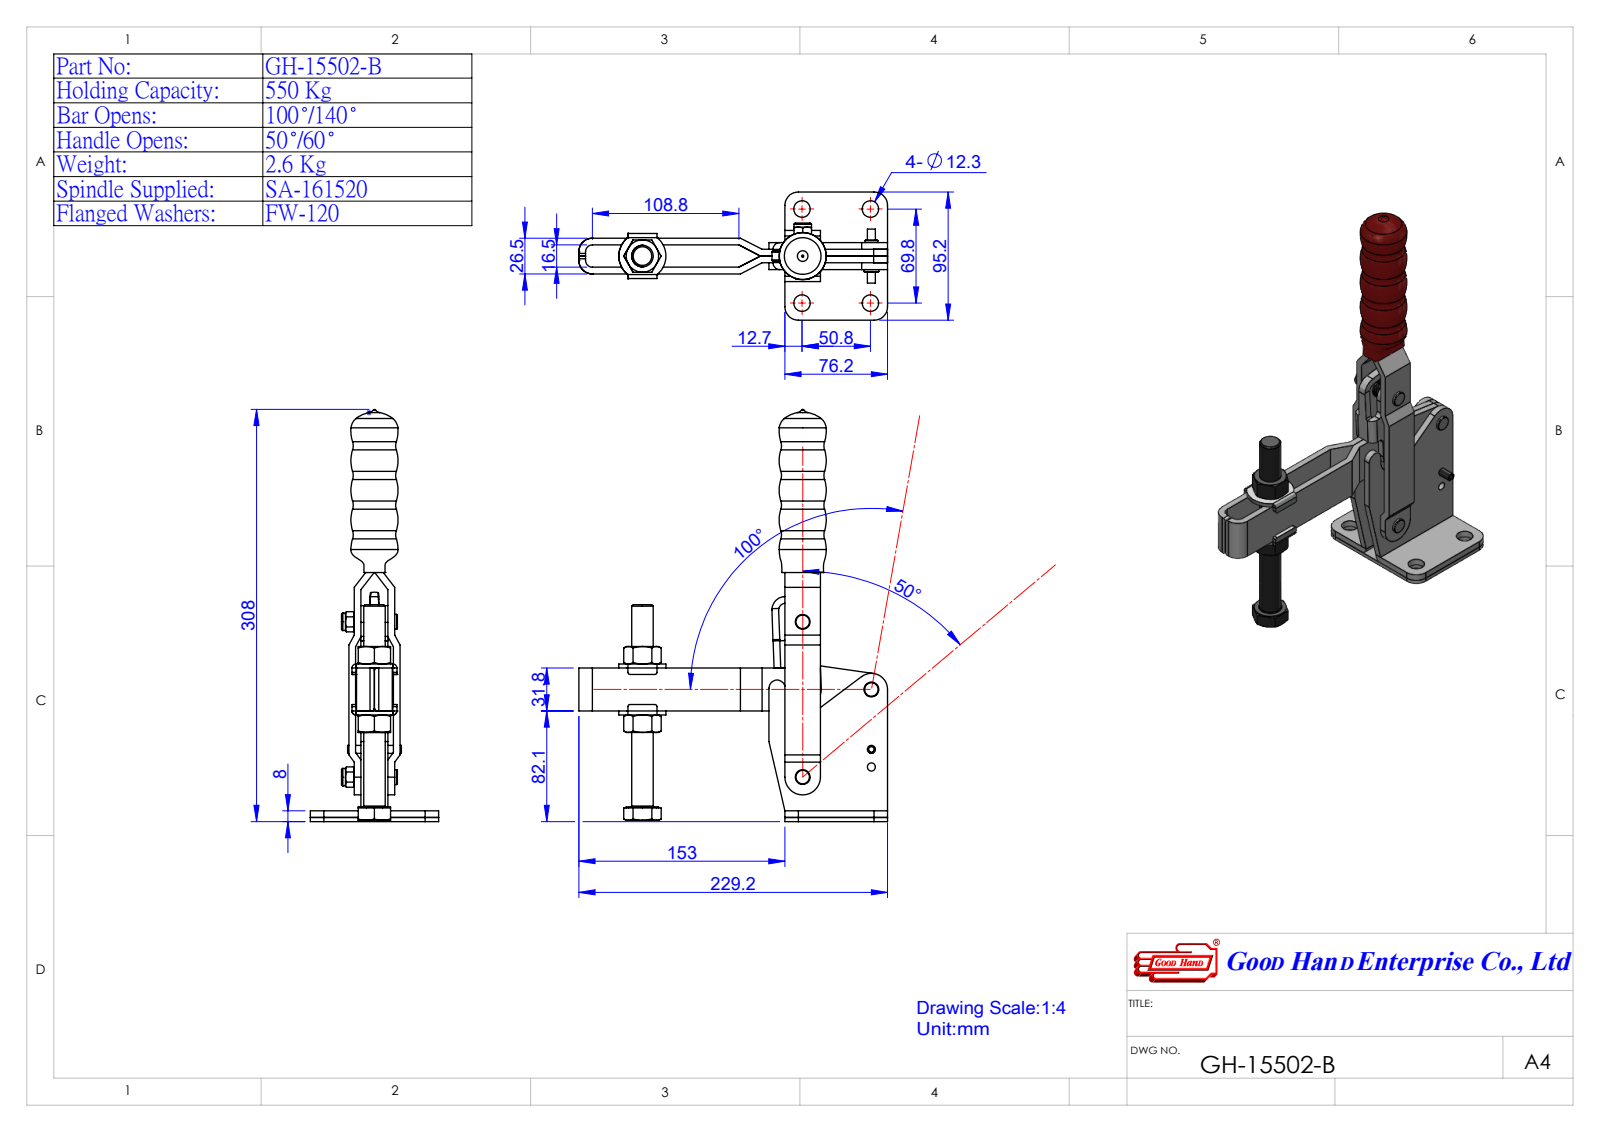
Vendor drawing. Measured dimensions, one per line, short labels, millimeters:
name: Group1^GH-15502-B(簡化)-1; Group2^GH-15502-B(簡化)-1; Group3^GH-15502-B(簡化)-1; Group4^GH-15502-B(簡化)-1 (+3 more)
written by: SolidWorks 2016 (AUTOMOTIVE_DESIGN)
unit: mm
bodies: 8 solids, 427 faces (180 planar, 131 cylindrical, 116 other)
size: 305.8 × 229.2 × 95.2
volume: 413 806 mm³; area: 143 804 mm²
holes: 4× ⌀7.5, 4× ⌀12.3, 1× ⌀6, 1× ⌀14, 1× ⌀16, 1× ⌀16.2
bosses: 2× ⌀10, 2× ⌀9.5, 2× ⌀9.45, 1× ⌀24, 1× ⌀6
rounds: 6× R10, 4× R1.5, 4× R3.01, 3× R12, 2× R3, 2× R5, 2× R11, 1× R6
face distances: 5, 15, 10, 3.25, 18.25, 20, 24, 23.25, 1.75, 5.75
hole spacings: 50.8, 69.8, 86.33, 123.51, 172.84, 49.25, 50.23, 51.55
